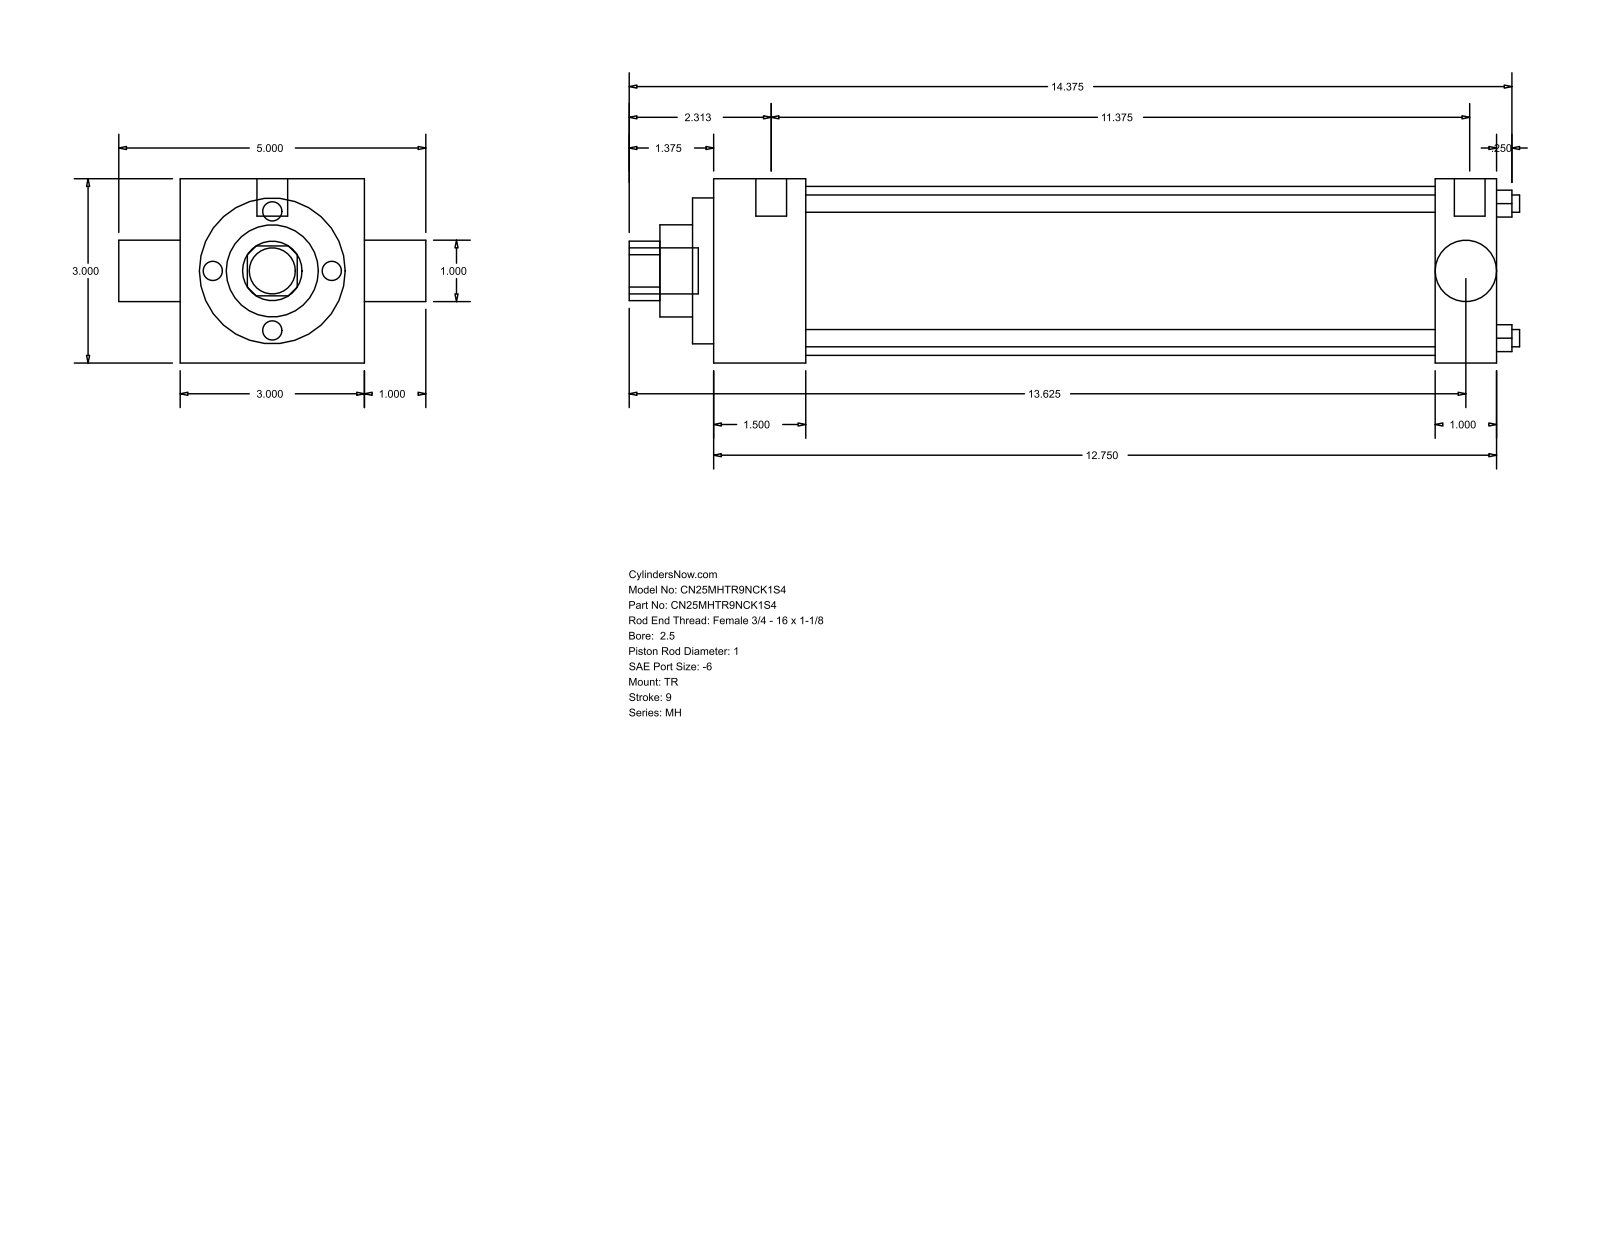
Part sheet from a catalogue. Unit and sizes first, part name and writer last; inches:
Units: inches
Overall size (bounding box): 14.5 × 5 × 3
Round holes (diameter × count): ⌀0.281 ×4, ⌀0.998 ×1, ⌀1 ×1, ⌀1.5 ×1, ⌀2.375 ×1, ⌀2.75 ×1
Round bosses / shafts (diameter × count): ⌀0.219 ×3, ⌀0.5 ×2, ⌀0.75 ×1
Partial cylindrical surfaces — rounded edges, fillets, slot ends (radius × count): R0.484 ×1
Main face-to-face distances: 3, 12.75, 1, 1.5, 11.25, 11.75, 10.25, 0.344, 1.844, 12.094
Hole centre spacings: 1.548, 2.19, 3.097
Bodies: 0 solids, 86 faces (61 planar, 25 cylindrical, 0 other)
Part name (STEP PRODUCT): MH_TR__0250_1
STEP written by: GSSL Pune (CONFIG_CONTROL_DESIGN)
